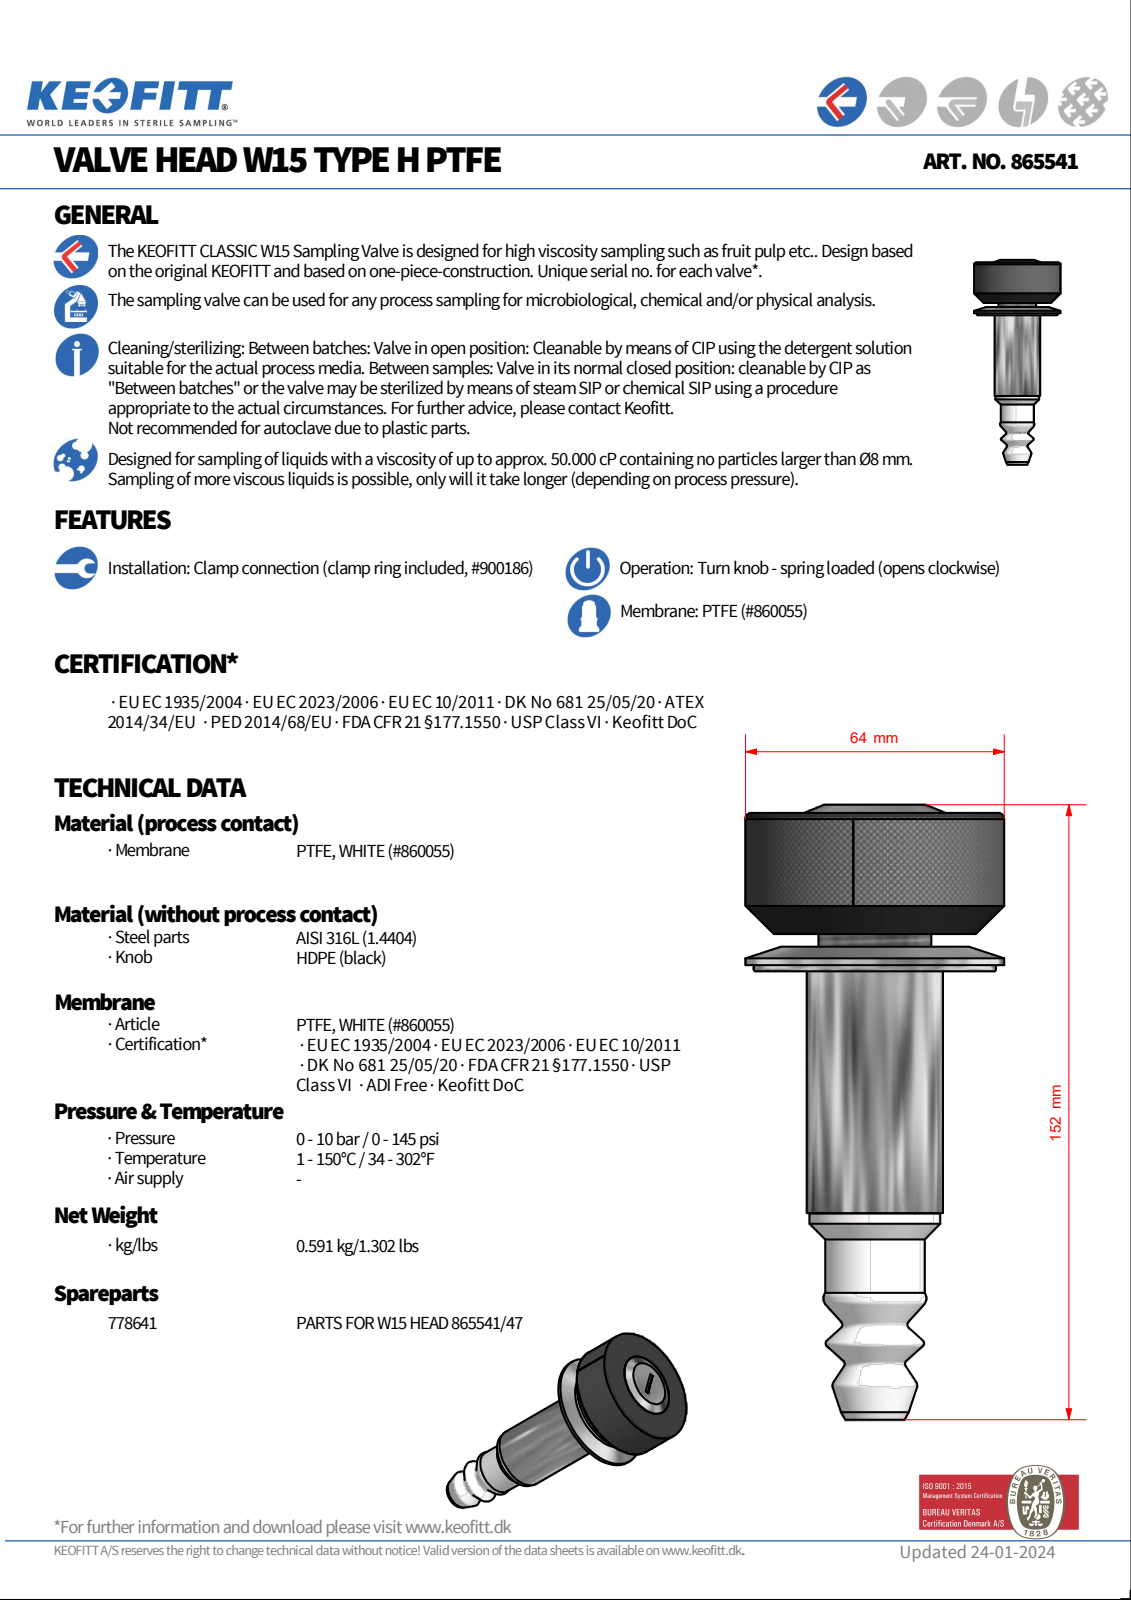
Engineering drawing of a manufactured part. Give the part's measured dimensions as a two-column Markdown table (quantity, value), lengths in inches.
| quantity | value |
| --- | --- |
| STEP written by | Autodesk Inventor 2008 (AUTOMOTIVE_DESIGN) |
| units | inches |
| bodies | 1 solid, 59 faces (20 planar, 21 cylindrical, 18 other) |
| overall size | 6.083 × 2.52 × 2.52 |
| volume | 11.44 in³ |
| surface area | 45.42 in² |
| round holes (diameter × count) | 0.484 × 1, 0.782 × 1, 1.114 × 1, 1.386 × 1 |
| round bosses / shafts (diameter × count) | 2.52 × 1, 2.52 × 1, 2.362 × 1, 1.378 × 1, 1.327 × 1, 1.276 × 1, 1.102 × 1, 0.97 × 1 |
| partial cylindrical surfaces (radius × count) | 0.039 × 1, 0.62 × 1, 0.984 × 1 |
| main face-to-face distances | 1.543, 0.362, 1.181, 0.24, 0.122, 1.303, 2.417, 2.657, 2.779, 3.96 |
